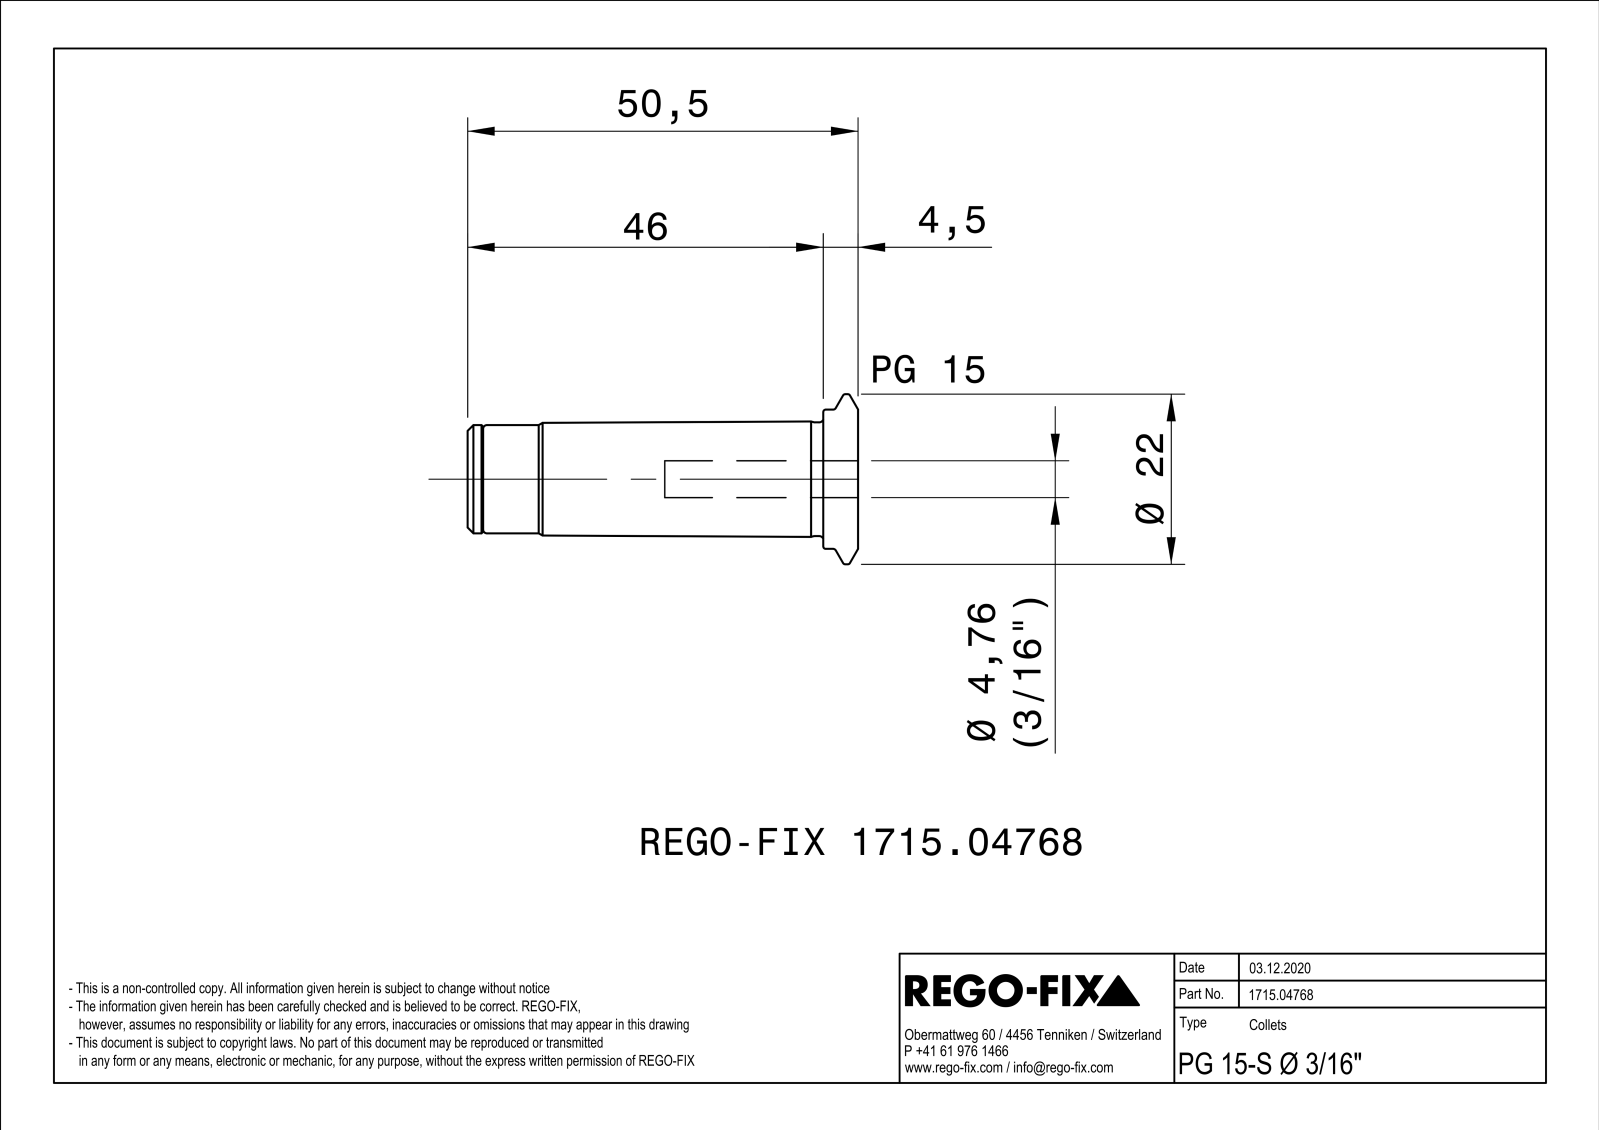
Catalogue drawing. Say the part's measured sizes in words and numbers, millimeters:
The part is named "0016405". Its 3-D file was written by "SIEMENS PLM Software Solid Edge ST10 (AUTOMOTIVE_DESIGN)". It is 1 solid with 121 faces: 39 planar, 26 cylindrical and 56 other. Overall it measures 50.5 by 22 by 21.99 millimeters. Its volume is 556 cubic millimeters and its surface area 5 535 square millimeters. Round holes: 1 of diameter 4.76, 1 of diameter 6.92, 1 of diameter 7.2, 1 of diameter 8.2, 1 of diameter 8.5, 1 of diameter 10.92, 1 of diameter 12.2. Round bosses or shafts: 1 of diameter 22, 1 of diameter 18, 1 of diameter 14.7, 1 of diameter 14. Partial cylindrical surfaces (rounded edges, fillets, slot ends): 1 of radius 5.2, 1 of radius 6. The main face-to-face distances are 1, 48.5, 5, 4, 2, 50.5, 8, 3, 42.5, 6.
